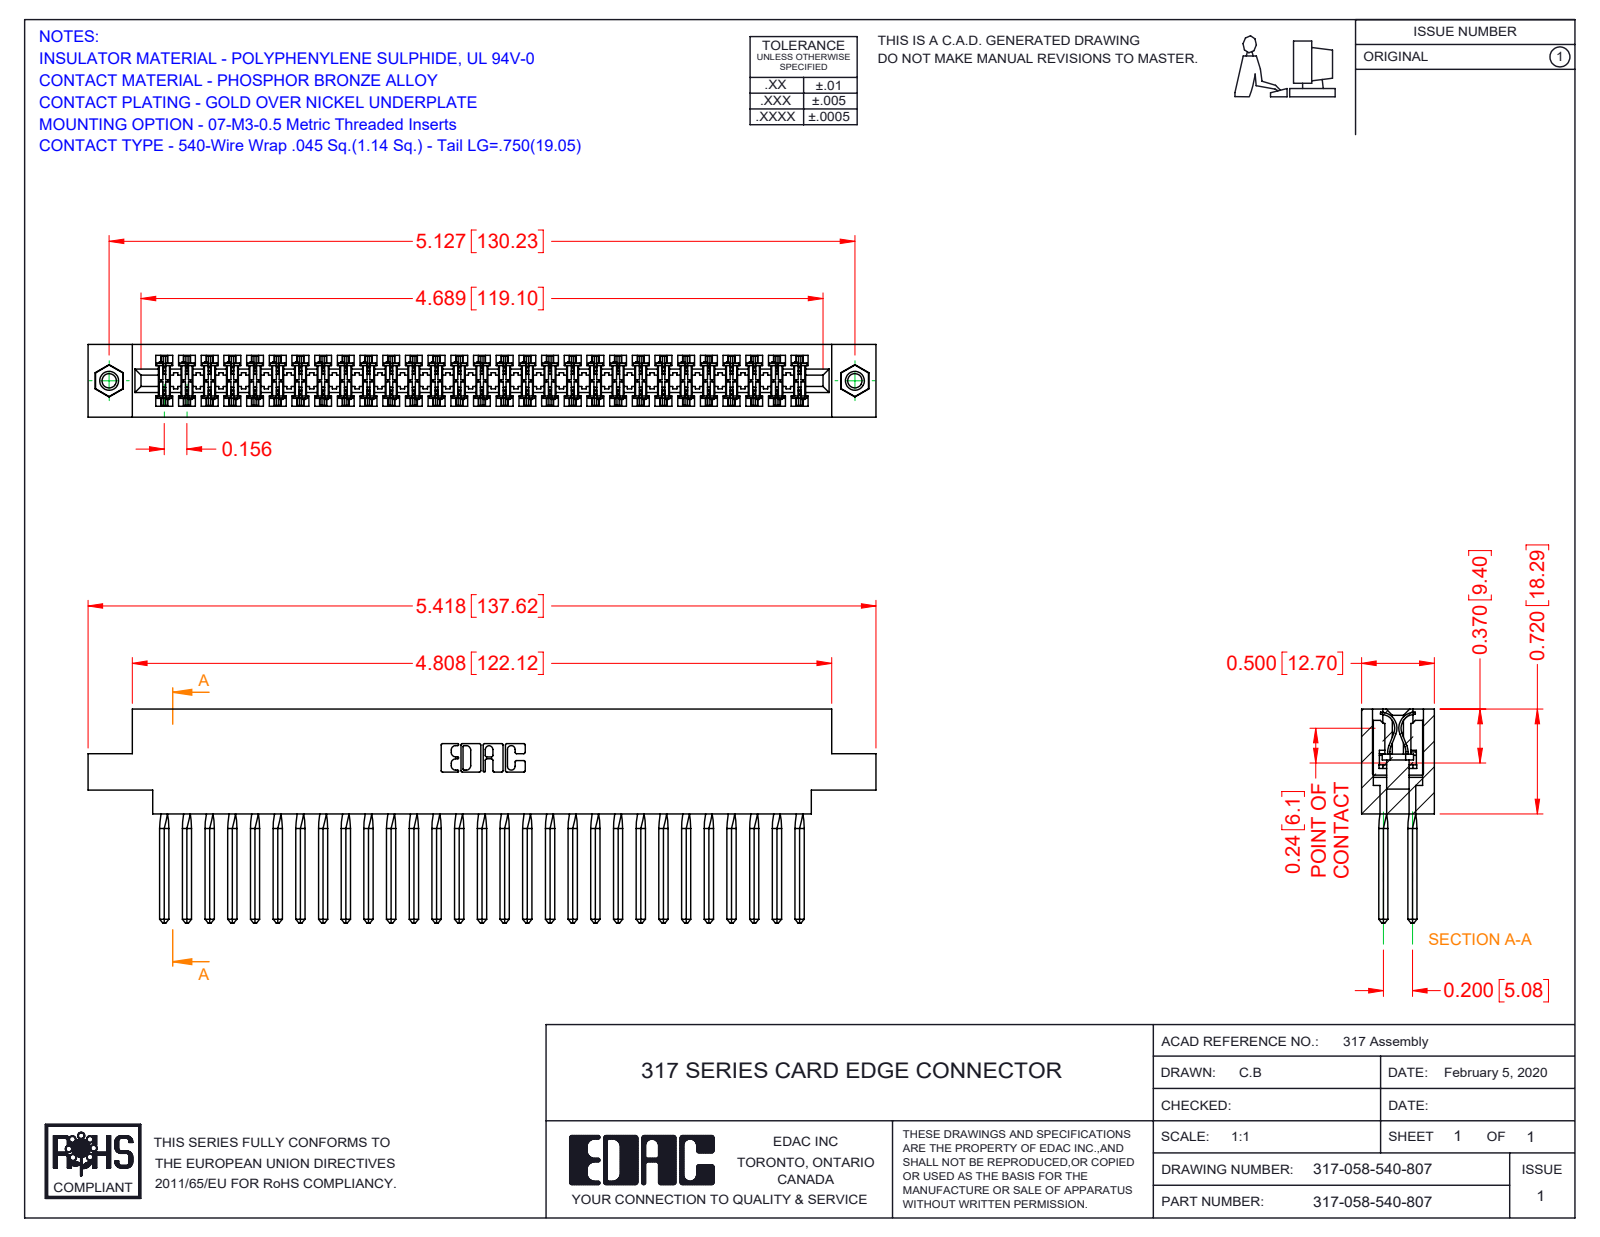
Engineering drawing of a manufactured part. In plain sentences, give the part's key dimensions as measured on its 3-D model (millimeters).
The part is named "345-250-001_345-250-005-103; 317-058-540-807; 317-290-001_540; 317 Part_.156 Dia - TI". Its 3-D file was written by "SolidWorks 2016 (CONFIG_CONTROL_DESIGN)". It is 61 solids with 5324 faces: 4324 planar, 752 cylindrical and 248 other. Overall it measures 137.6 by 37.3 by 12.7 millimeters. Its volume is 22 650 cubic millimeters and its surface area 33 300 square millimeters. Round holes: 2 of diameter 2.5, 2 of diameter 3.2, 2 of diameter 4. Round bosses or shafts: 2 of diameter 3.9. Partial cylindrical surfaces (rounded edges, fillets, slot ends): 116 of radius 0.4, 22 of radius 0.3, 6 of radius 0.2, 6 of radius 0.8, 3 of radius 0.7, 2 of radius 2.4, 2 of radius 2.5, 2 of radius 2.8. The main face-to-face distances are 12.7, 1.9, 10.8, 8.9, 2.8, 5, 2.4, 5.1, 18.3, 2.9. The hole center spacings are 130.2.
